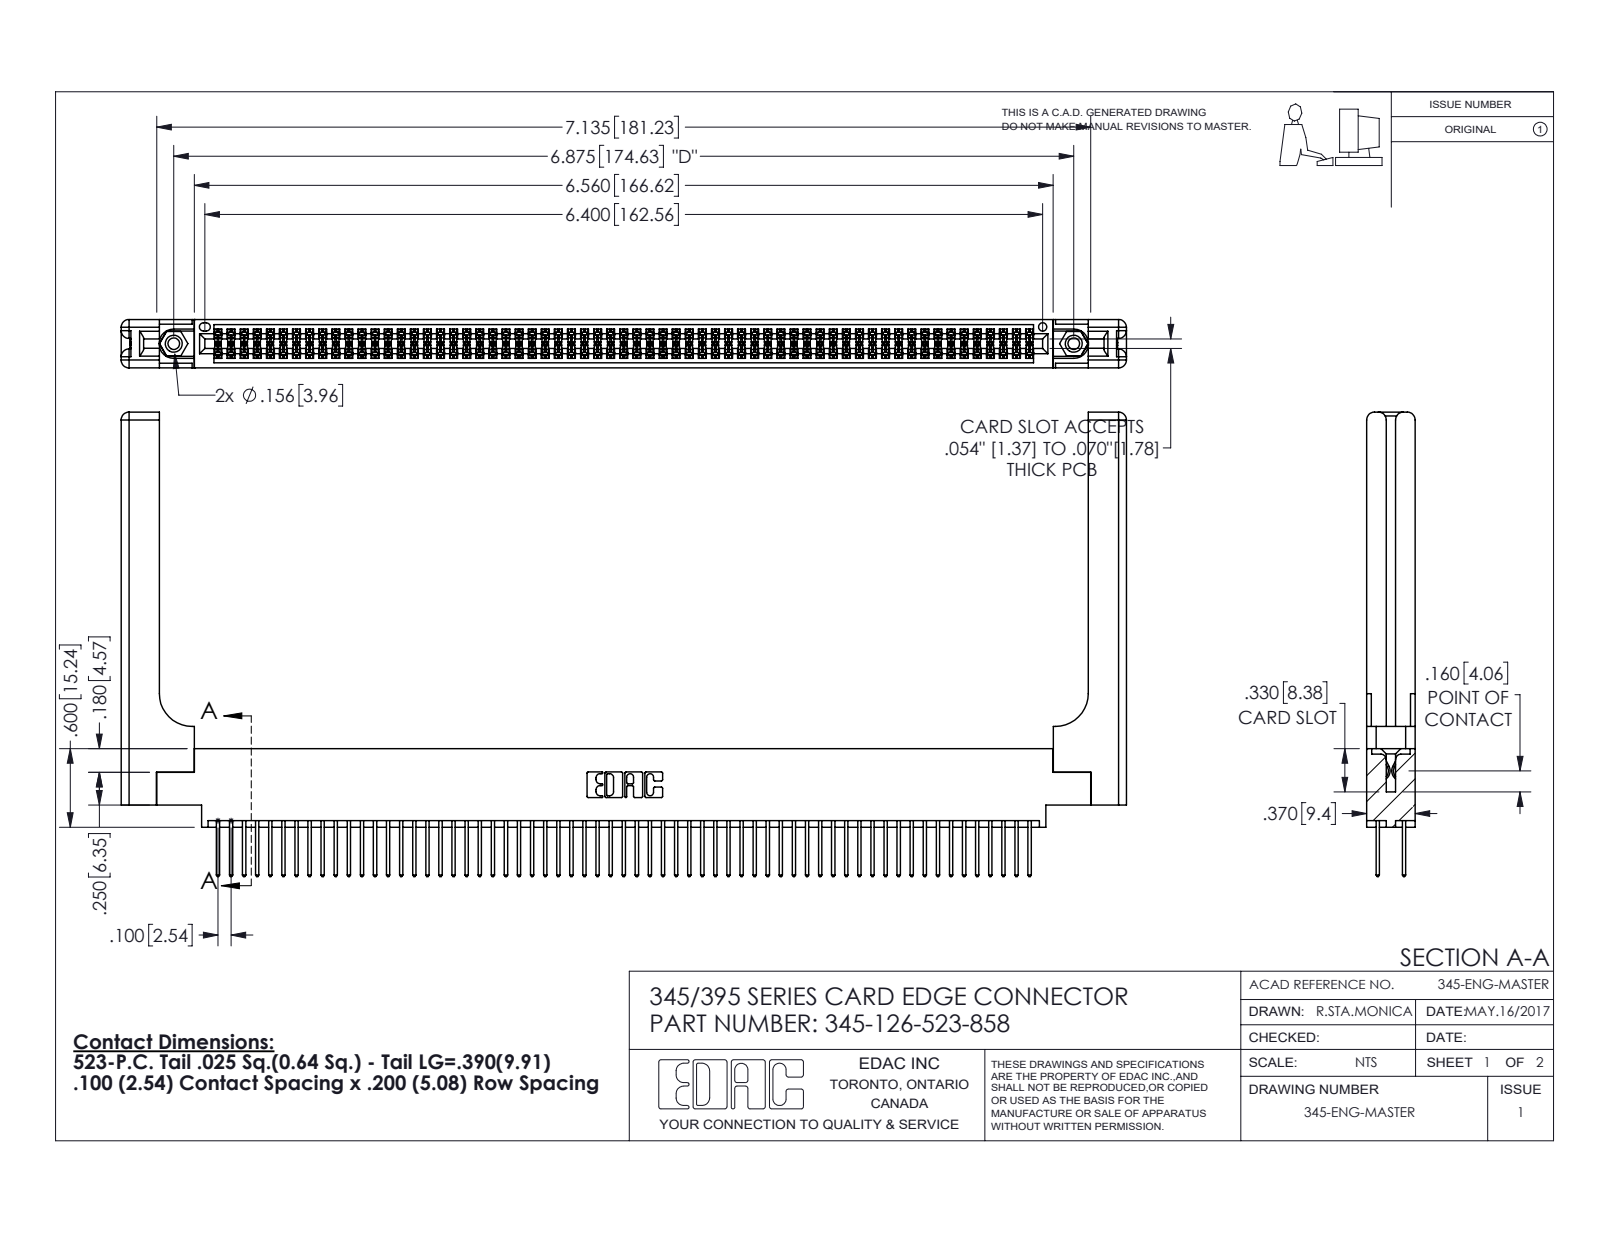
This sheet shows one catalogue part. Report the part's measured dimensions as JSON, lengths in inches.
{"part_name": "345-220-058_345-220-058; 345-292-001_345-293-123; 345 Part_0.170 Offset - 0.156 Dia-TH; 345-126-523-858 (+1 more)", "step_written_by": "SolidWorks 2016 (CONFIG_CONTROL_DESIGN)", "units": "inches", "bodies": {"solids": 131, "faces": 6686, "planar": 4390, "cylindrical": 2236, "other": 60}, "overall_size": [7.679, 3.547, 0.37], "volume_in3": 1.694, "surface_area_in2": 54.68, "round_holes": [[0.089, 2], [0.125, 2], [0.156, 2], [0.064, 1]], "round_bosses_or_shafts": [[0.155, 2]], "partial_cylinders_radius": [[0.006, 189], [0.01, 126], [0.01, 22], [0.06, 16], [0.007, 6], [0.031, 6], [0.026, 3], [0.014, 2]], "face_to_face_distances": [0.072, 0.298, 0.37, 0.098, 0.272, 0.025, 0.2, 0.225, 0.175, 0.148], "hole_center_spacings": [0.27, 6.639, 6.875]}
